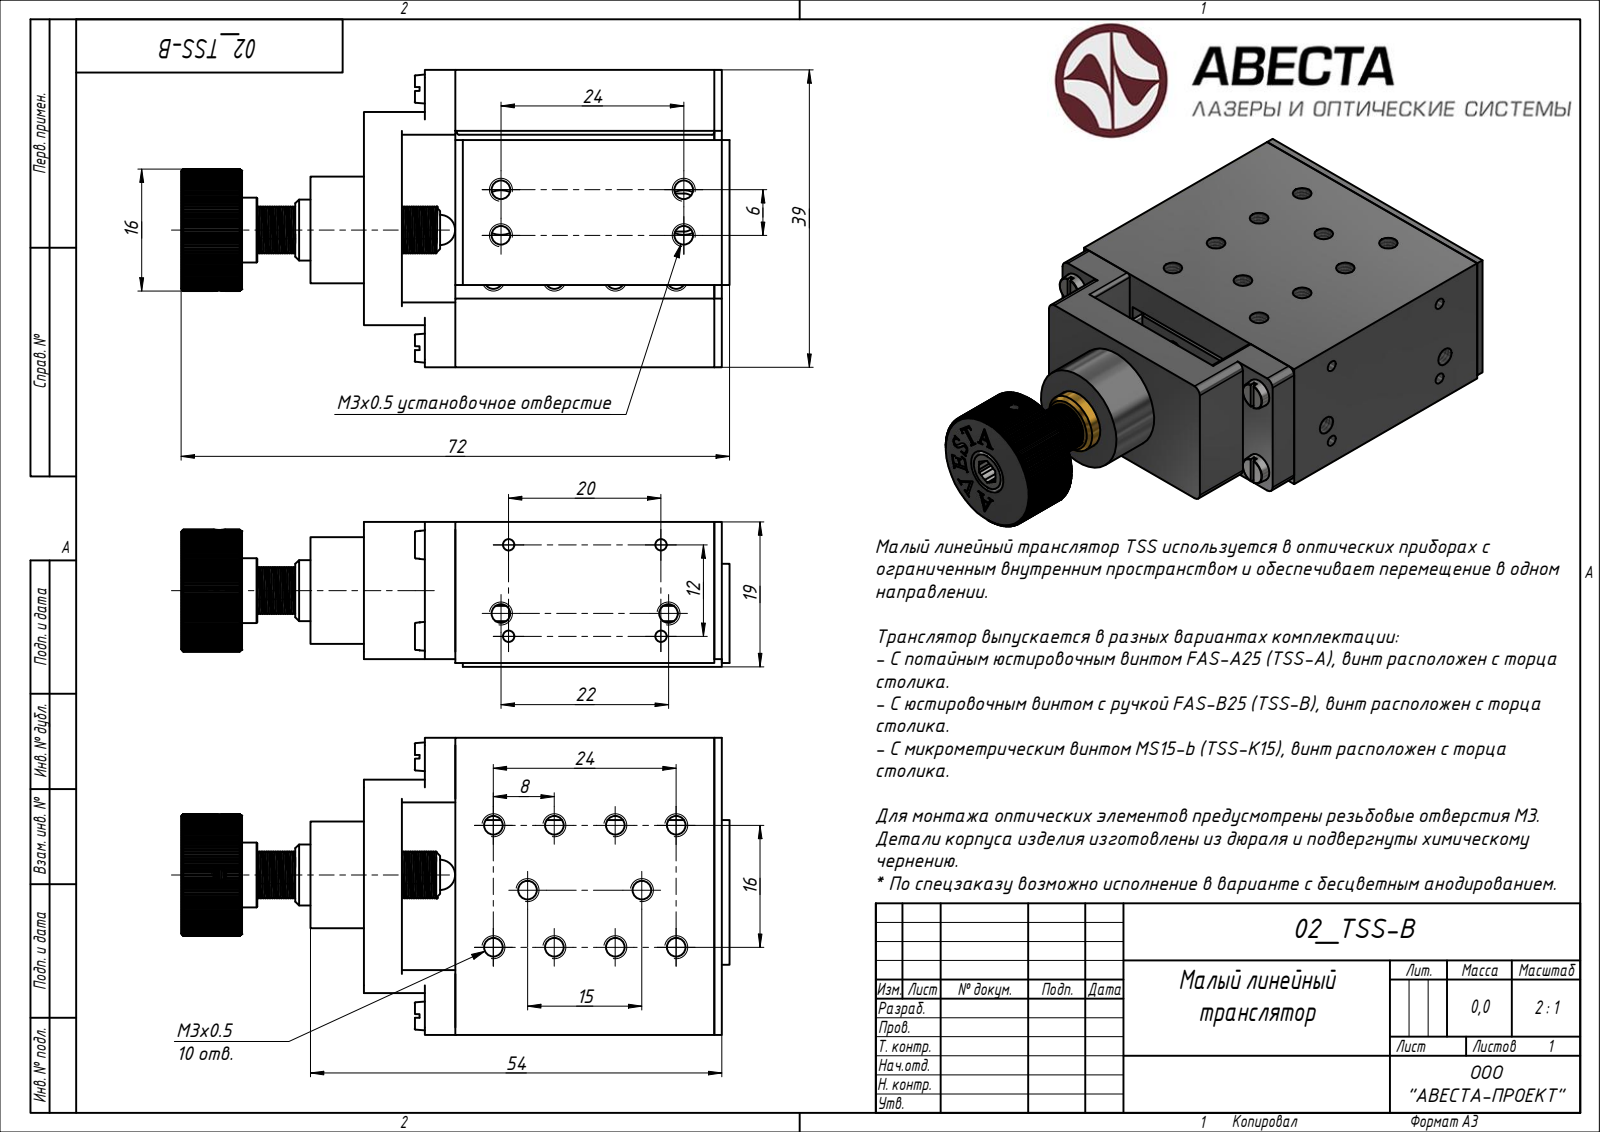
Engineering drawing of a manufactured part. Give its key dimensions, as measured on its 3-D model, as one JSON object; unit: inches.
{"step_written_by": "Rhino 7.34 (AUTOMOTIVE_DESIGN)", "units": "inches", "bodies": {"solids": 4, "faces": 1165, "planar": 609, "cylindrical": 356, "other": 200}, "overall_size": [2.835, 1.535, 0.748], "volume_in3": 1.666, "surface_area_in2": 30.43, "round_holes": [[0.097, 15], [0.098, 6], [0.062, 5], [0.059, 4], [0.062, 4], [0.097, 3], [0.122, 1], [0.236, 1], [0.374, 1]], "round_bosses_or_shafts": [[0.157, 8], [0.551, 1], [0.354, 1], [0.335, 1], [0.315, 1], [0.236, 1], [0.062, 1]], "partial_cylinders_radius": [[0.039, 8], [0.02, 4], [0.079, 4], [0.031, 3], [0.048, 2], [0.048, 2], [0.014, 1], [0.031, 1]], "face_to_face_distances": [0.02, 0.472, 0.197, 0.531, 0.079, 0.039, 0.276, 0.059, 0.453, 0.512], "hole_center_spacings": [0.63, 0.315, 0.704, 0.276, 0.472, 0.891, 0.124, 0.231]}
